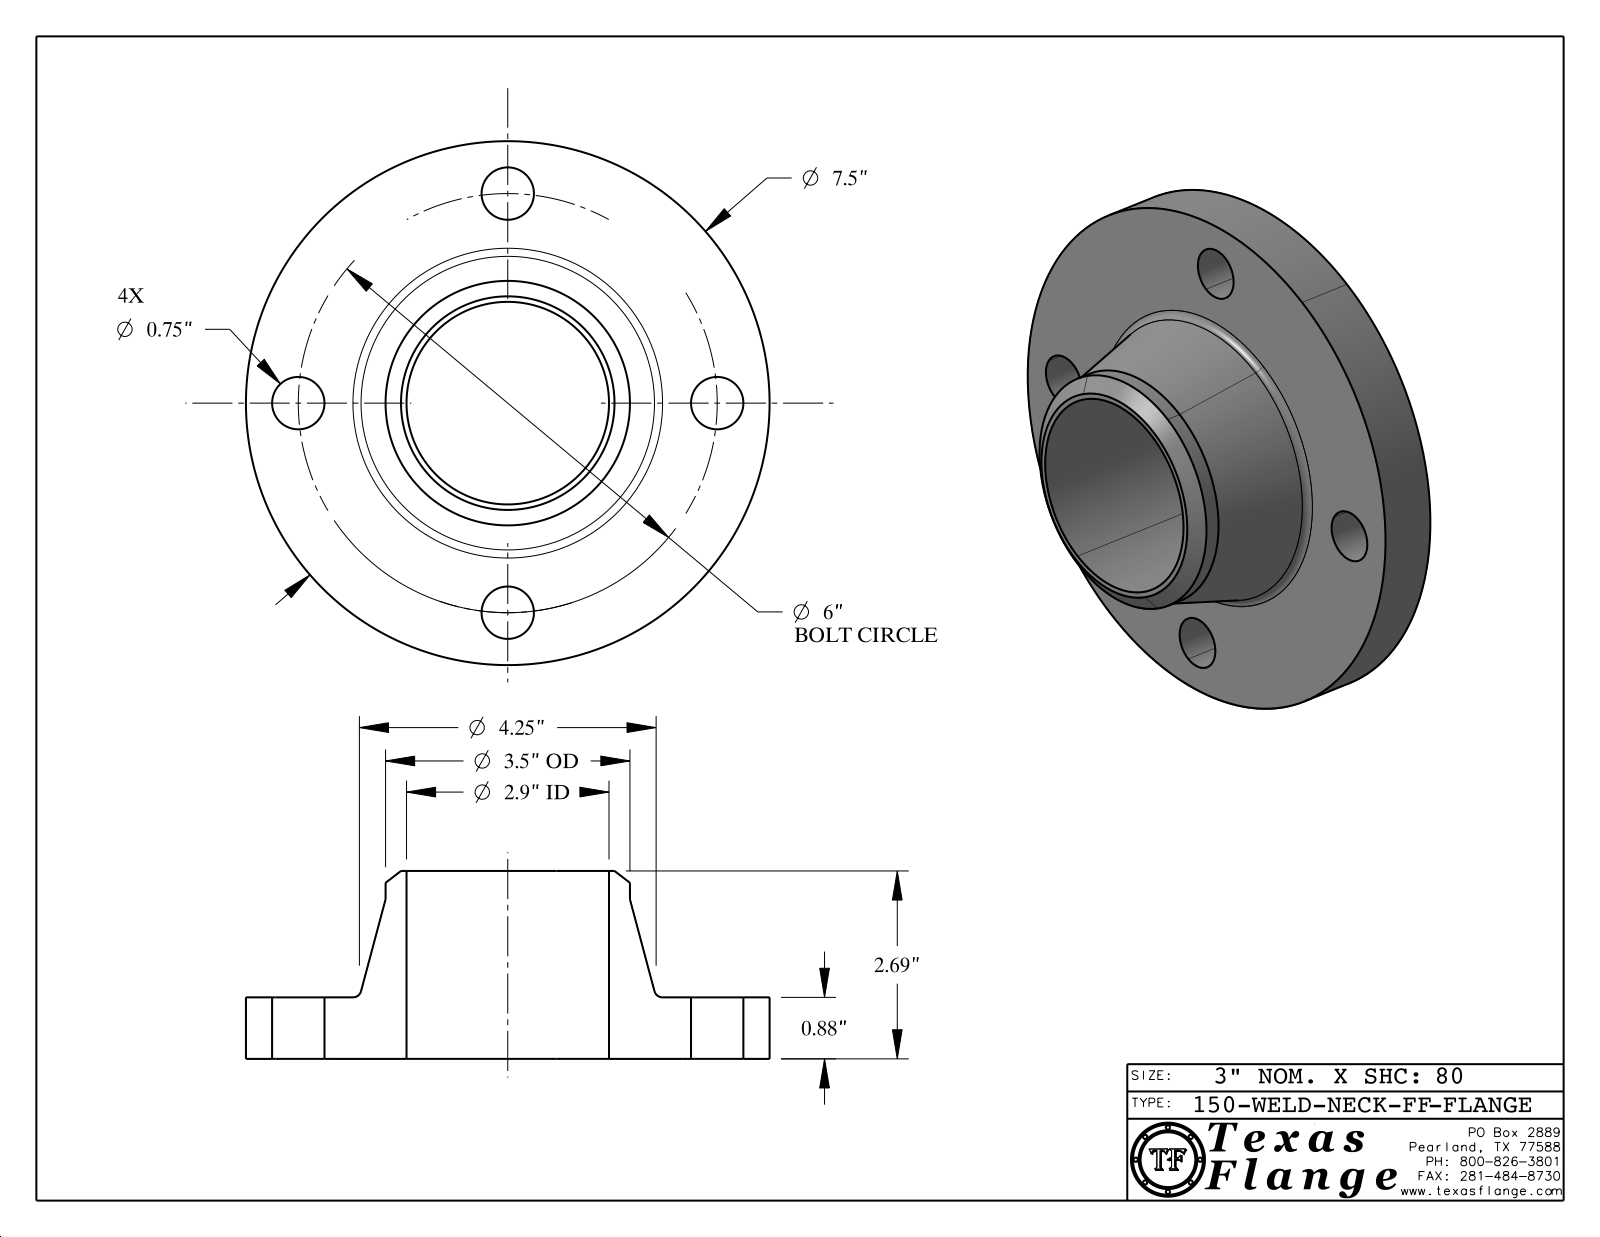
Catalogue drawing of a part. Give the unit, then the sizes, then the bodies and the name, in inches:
Units: inches
Overall size (bounding box): 7.5 × 7.5 × 2.69
Round holes (diameter × count): ⌀0.75 ×4, ⌀0.495 ×1, ⌀2.9 ×1
Round bosses / shafts (diameter × count): ⌀0.03 ×8, ⌀7.5 ×1, ⌀3.5 ×1, ⌀0.39 ×1
Main face-to-face distances: 0.88, 2.69, 1.81, 0.865, 0.015, 1.825, 0.148, 0.144, 0.027, 0.096
Hole centre spacings: 3, 4.243, 2.296, 5.543, 6
Volume: 39.89 in³ · Surface area: 141.2 in²
Bodies: 1 solid, 409 faces (369 planar, 34 cylindrical, 6 other)
Part name (STEP PRODUCT): 150-WELD-NECK-FF
STEP written by: CATIA V5 STEP AP214 (AUTOMOTIVE_DESIGN)
